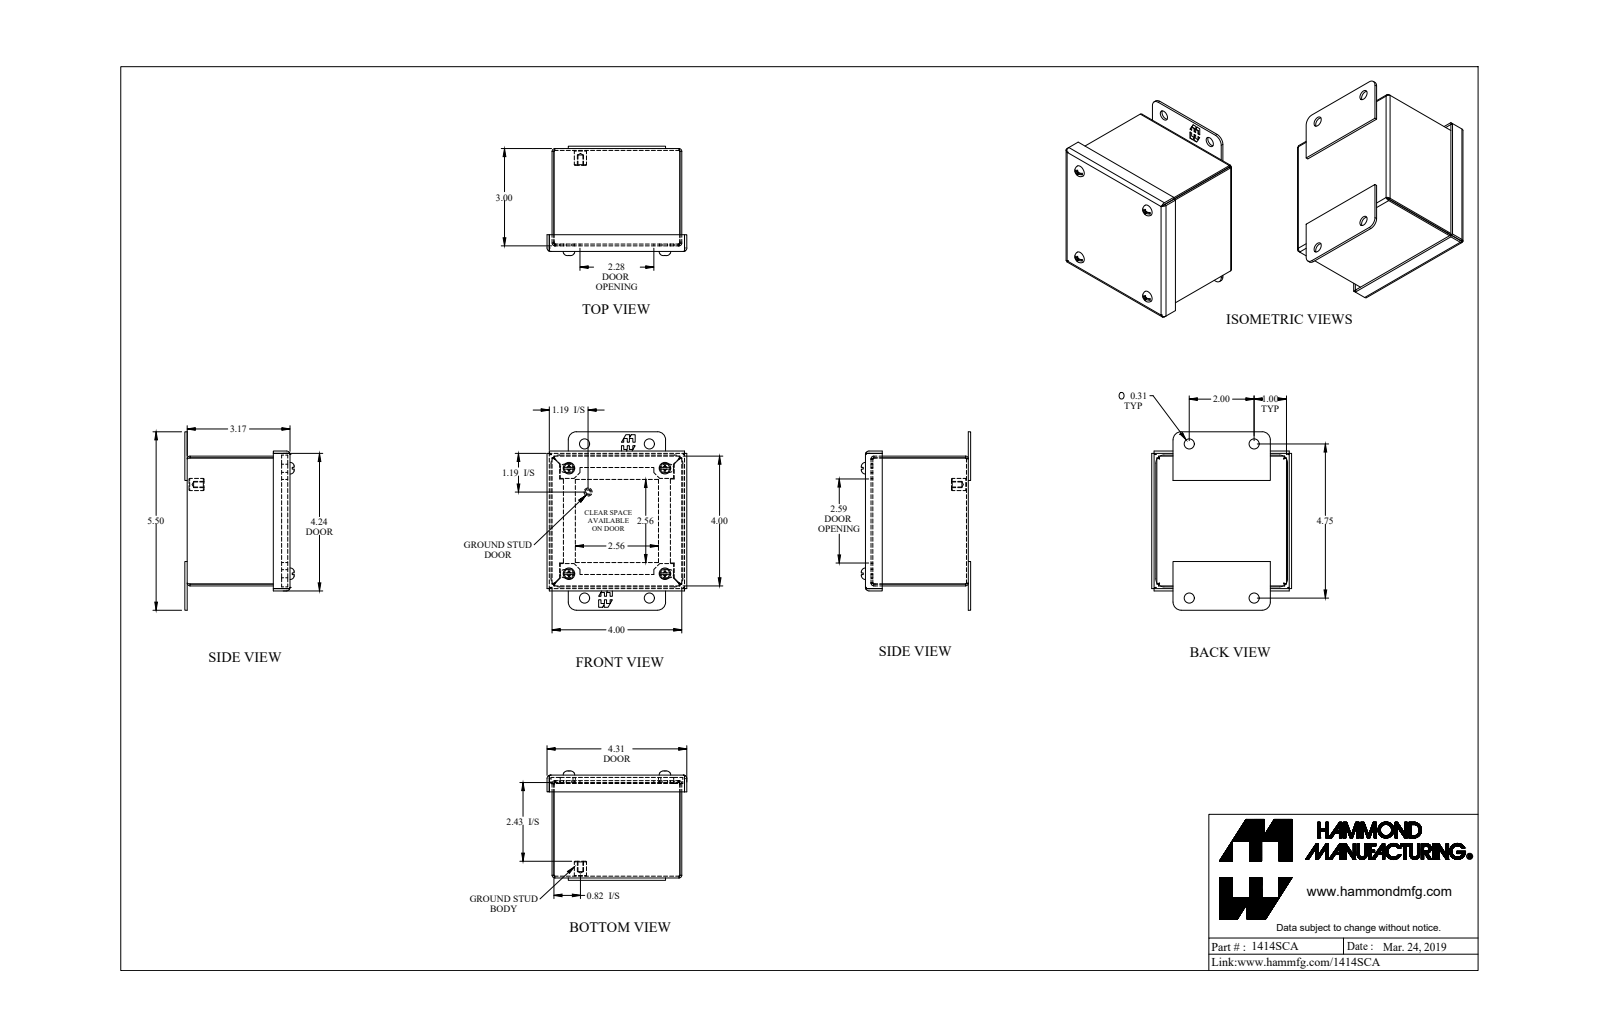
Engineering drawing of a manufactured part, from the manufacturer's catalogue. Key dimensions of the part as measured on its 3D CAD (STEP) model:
Part name (STEP PRODUCT): 1414SCA
STEP written by: SolidWorks 2018 (AUTOMOTIVE_DESIGN)
Units: inches
Bodies: 19 solids, 518 faces (354 planar, 120 cylindrical, 44 other)
Overall size (bounding box): 5.5 × 4.312 × 3.371
Volume: 8.212 in³ · Surface area: 241 in²
Round holes (diameter × count): ⌀0.159 ×4, ⌀0.313 ×4, ⌀0.156 ×1
Round bosses / shafts (diameter × count): ⌀0.39 ×4, ⌀0.19 ×4, ⌀0.148 ×4, ⌀0.275 ×3, ⌀0.375 ×1, ⌀0.275 ×1, ⌀0.25 ×1, ⌀0.188 ×1
Partial cylindrical surfaces — rounded edges, fillets, slot ends (radius × count): R0.125 ×12, R0.188 ×10, R0.029 ×8, R0.086 ×8, R0.25 ×8, R0.01 ×4, R0.039 ×4, R0.079 ×4
Main face-to-face distances: 0.057, 3.943, 3.172, 0.069, 3.886, 4, 0.072, 3.104, 3.115, 3.046
Hole centre spacings: 2, 2.956, 3.249, 4.392, 4.75, 5.154, 0.613, 0.886
